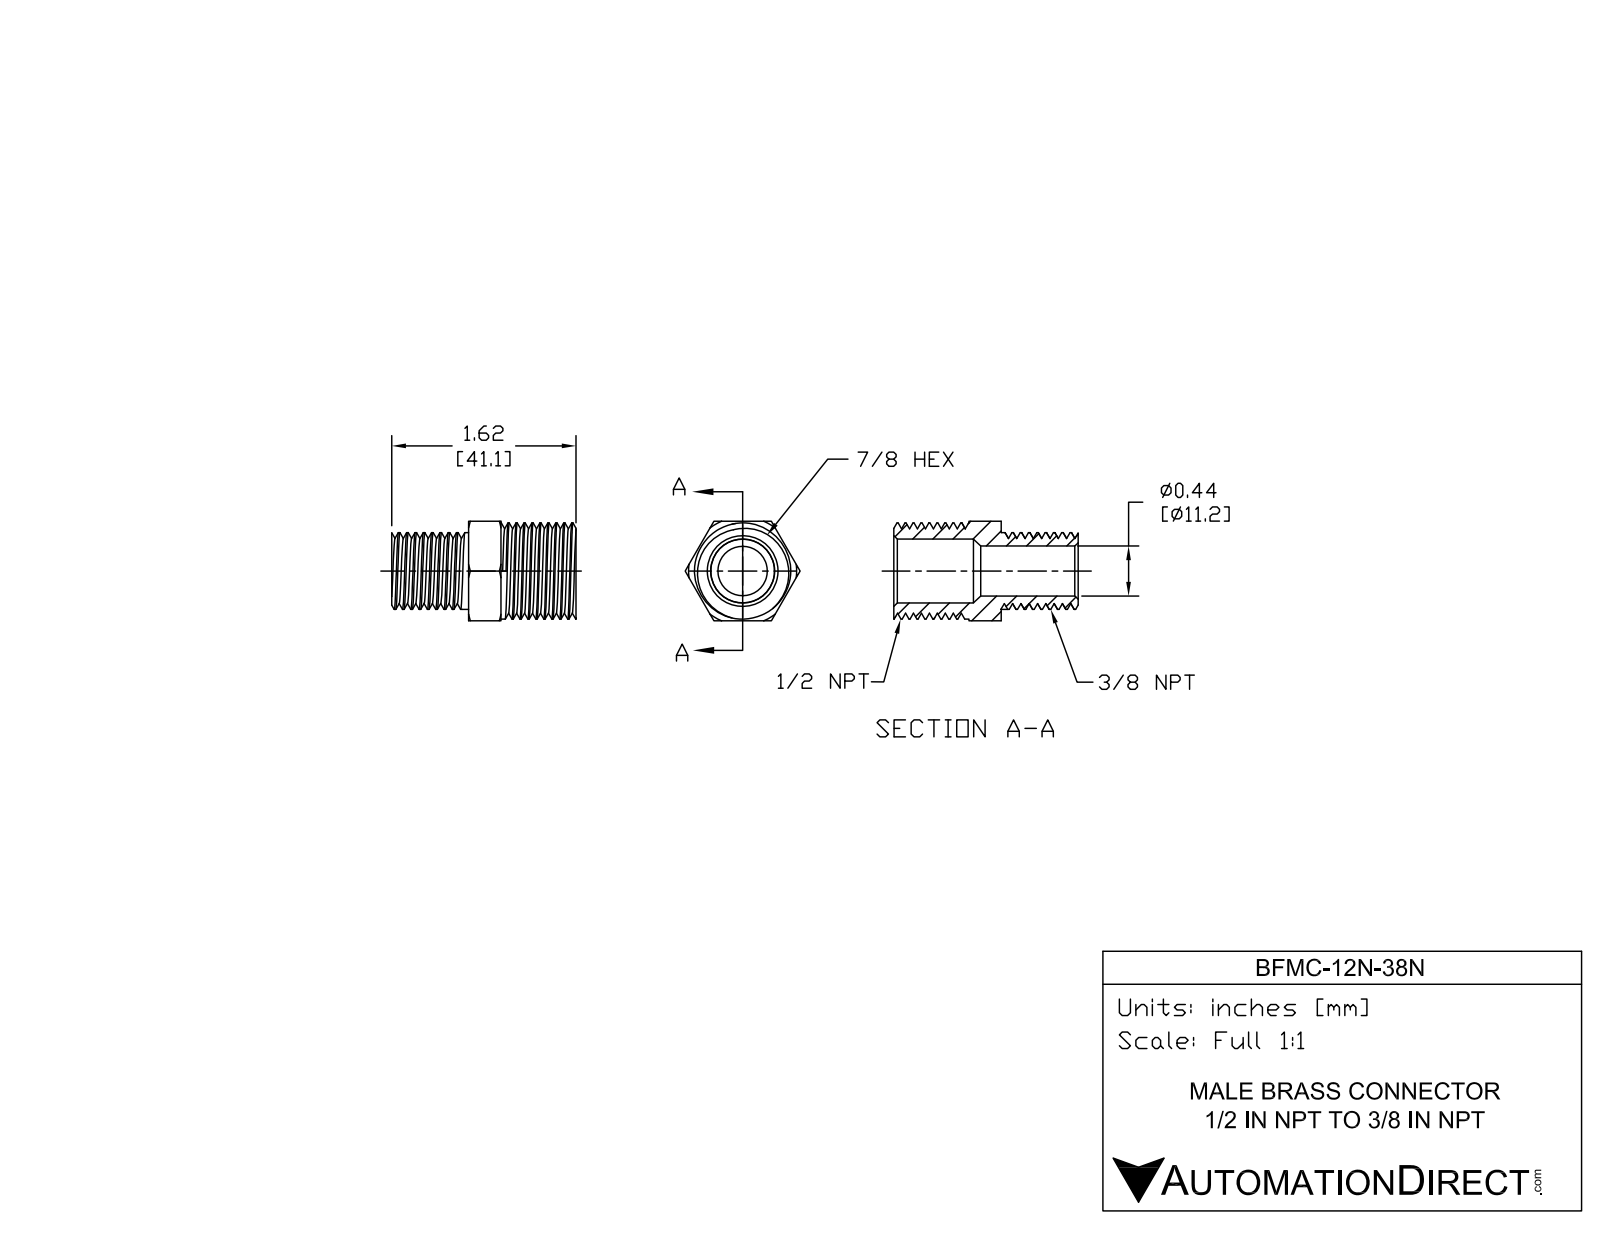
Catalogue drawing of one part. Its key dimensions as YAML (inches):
part_name: "BFMC-12N-38N"
step_written_by: "SolidWorks 2015 (CONFIG_CONTROL_DESIGN)"
units: inches
bodies: {solids: 1, faces: 83, planar: 13, cylindrical: 44, other: 26}
overall_size: [1.62, 1.01, 0.875]
volume: 0.422
surface_area: 9.621
round_holes:
  - {diameter: 0.434, count: 1}
  - {diameter: 0.562, count: 1}
round_bosses_or_shafts:
  - {diameter: 0.845, count: 1}
  - {diameter: 0.675, count: 1}
face_to_face_distances: [0.875, 0.944, 0.676, 1.62, 0.96, 0.284, 0.66, 0.437, 0.92, 0.244]
